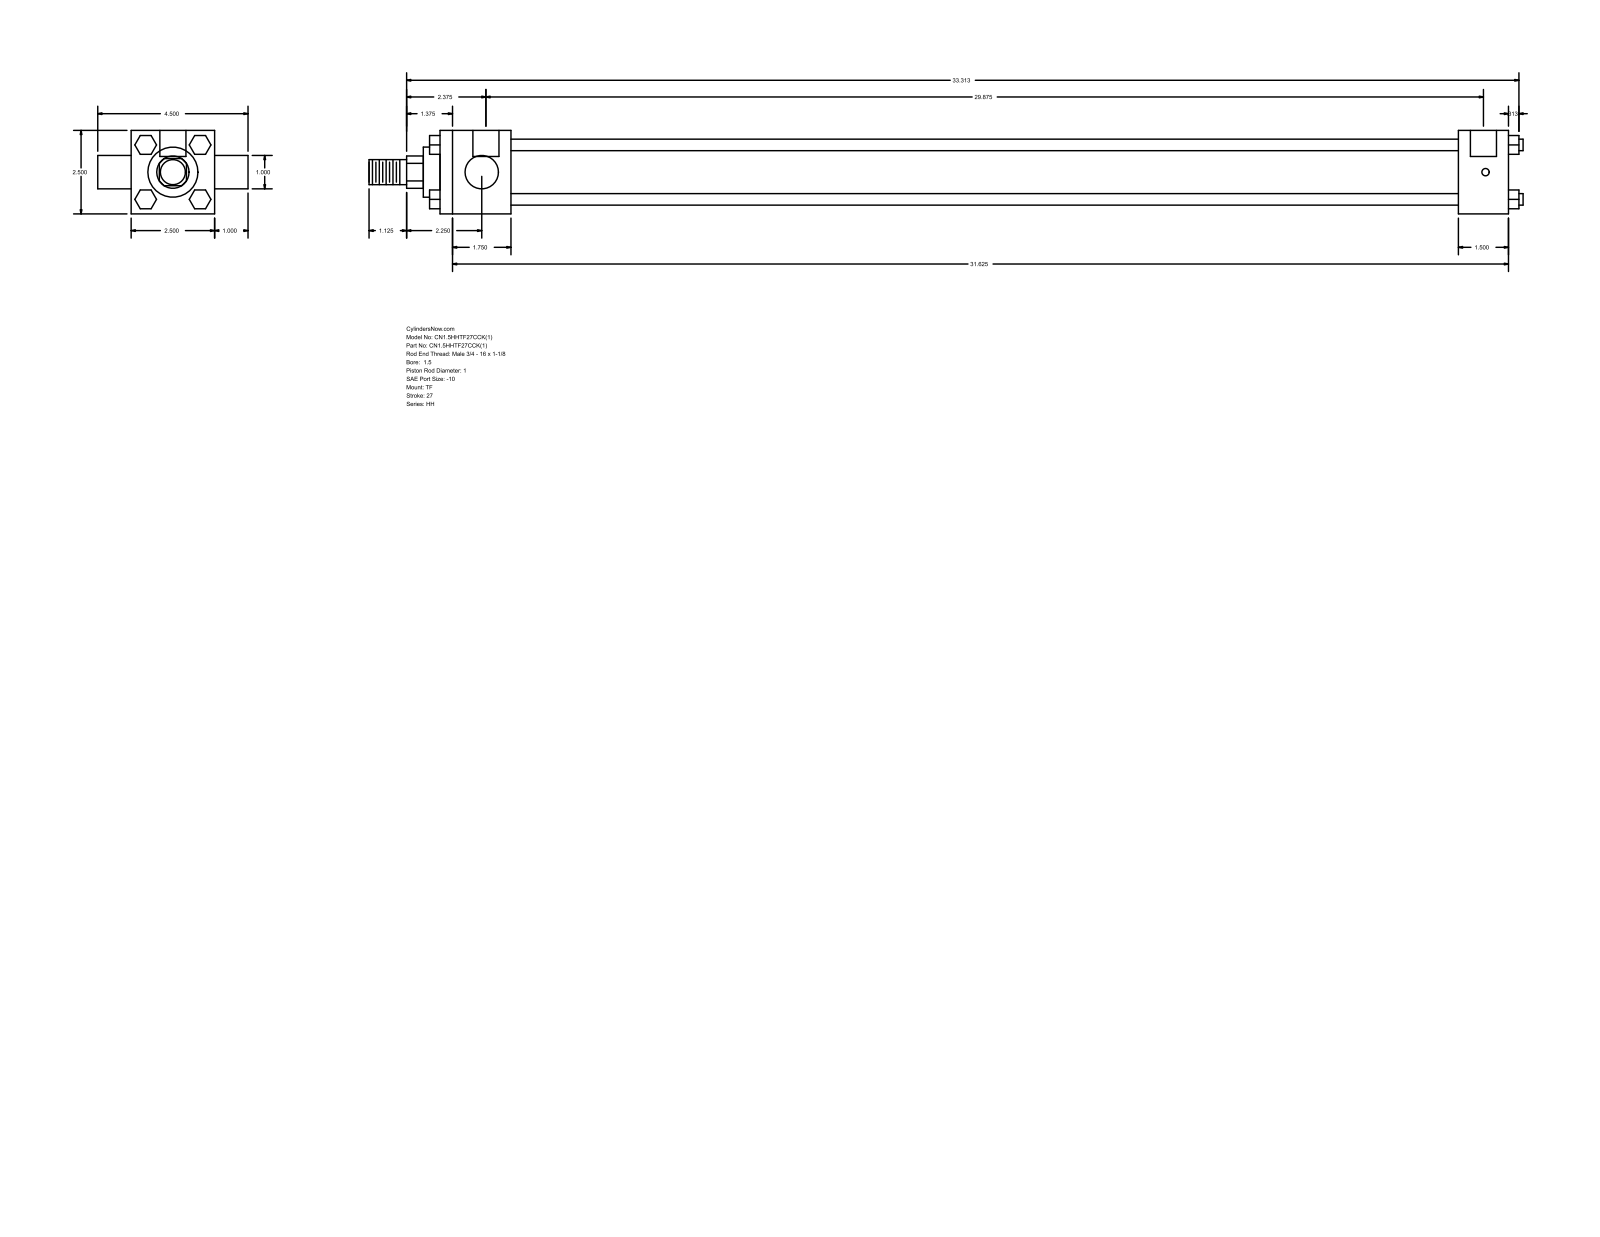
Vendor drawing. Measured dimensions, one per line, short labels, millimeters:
name: HH_TF__0150_1
written by: GSSL Pune (CONFIG_CONTROL_DESIGN)
unit: mm
bodies: 0 solids, 120 faces (92 planar, 28 cylindrical, 0 other)
size: 877.89 × 114.3 × 63.5
holes: 3× ⌀5.56, 2× ⌀19.84
bosses: 4× ⌀8.76, 2× ⌀25.4, 1× ⌀44.45, 1× ⌀38.1, 1× ⌀19.05
rounds: 1× R12.29
face distances: 63.5, 38.1, 758.82, 720.72, 53.98, 774.7, 812.8, 25.4, 20.7, 14.29
hole spacings: 1.59, 760.41, 758.82, 762
